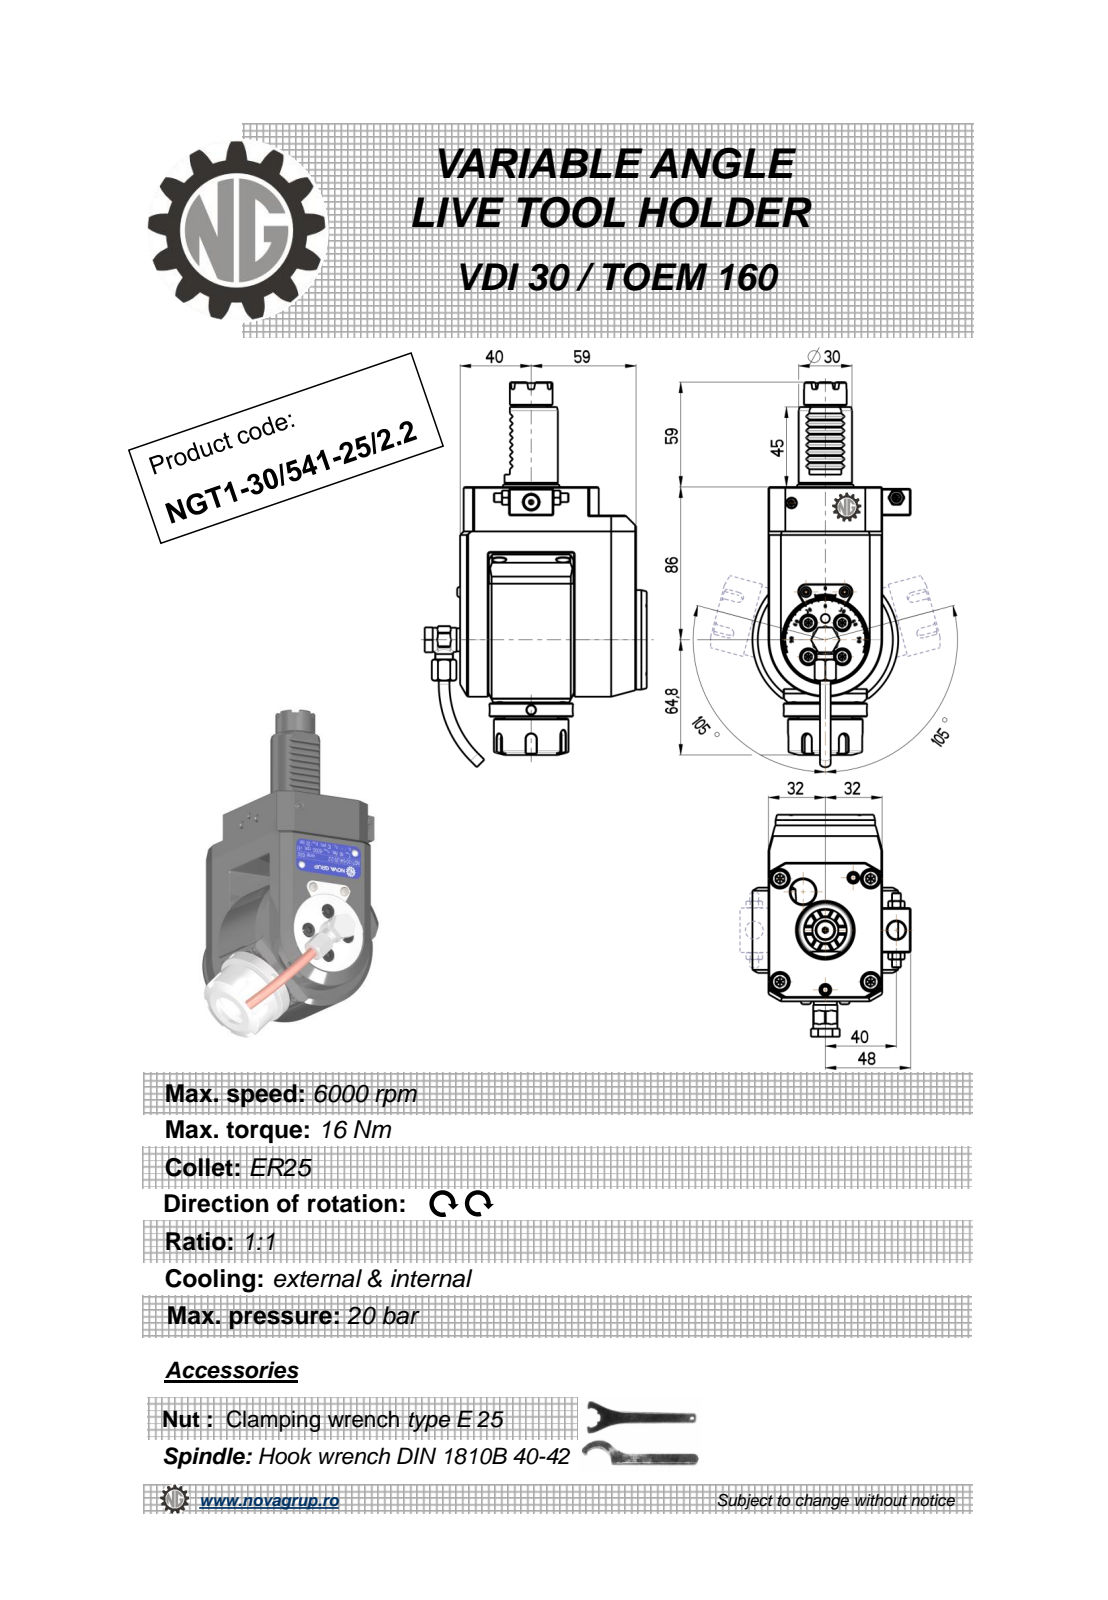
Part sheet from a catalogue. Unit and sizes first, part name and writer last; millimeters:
Units: millimetres
Overall size (bounding box): 216.67 × 124.9 × 89
Round holes (diameter × count): ⌀4 ×3, ⌀5 ×2, ⌀10 ×2, ⌀3 ×1, ⌀4.2 ×1, ⌀6.2 ×1, ⌀9 ×1, ⌀9.5 ×1, ⌀11 ×1, ⌀20.3 ×1
Round bosses / shafts (diameter × count): ⌀6 ×2, ⌀5.7 ×2, ⌀56 ×1, ⌀47 ×1, ⌀42 ×1, ⌀35 ×1, ⌀30 ×1, ⌀24 ×1
Partial cylindrical surfaces — rounded edges, fillets, slot ends (radius × count): R0.26 ×12, R0.3 ×8, R0.16 ×6, R3 ×5, R0.5 ×4, R1 ×2, R7.6 ×1, R7.7 ×1
Main face-to-face distances: 64, 16, 37, 6, 99, 105, 14, 62, 21, 83
Hole centre spacings: 0.4, 39.45, 40, 49, 49.4, 63.25, 63.56, 89.44
Volume: 800 141 mm³ · Surface area: 75 434 mm²
Bodies: 1 solid, 601 faces (262 planar, 140 cylindrical, 199 other)
Part name (STEP PRODUCT): NGT1_30_541_25_2_2
STEP written by: PRO/ENGINEER BY PARAMETRIC TECHNOLOGY CORPORATION, 2010280 (CONFIG_CONTROL_DESIGN)
